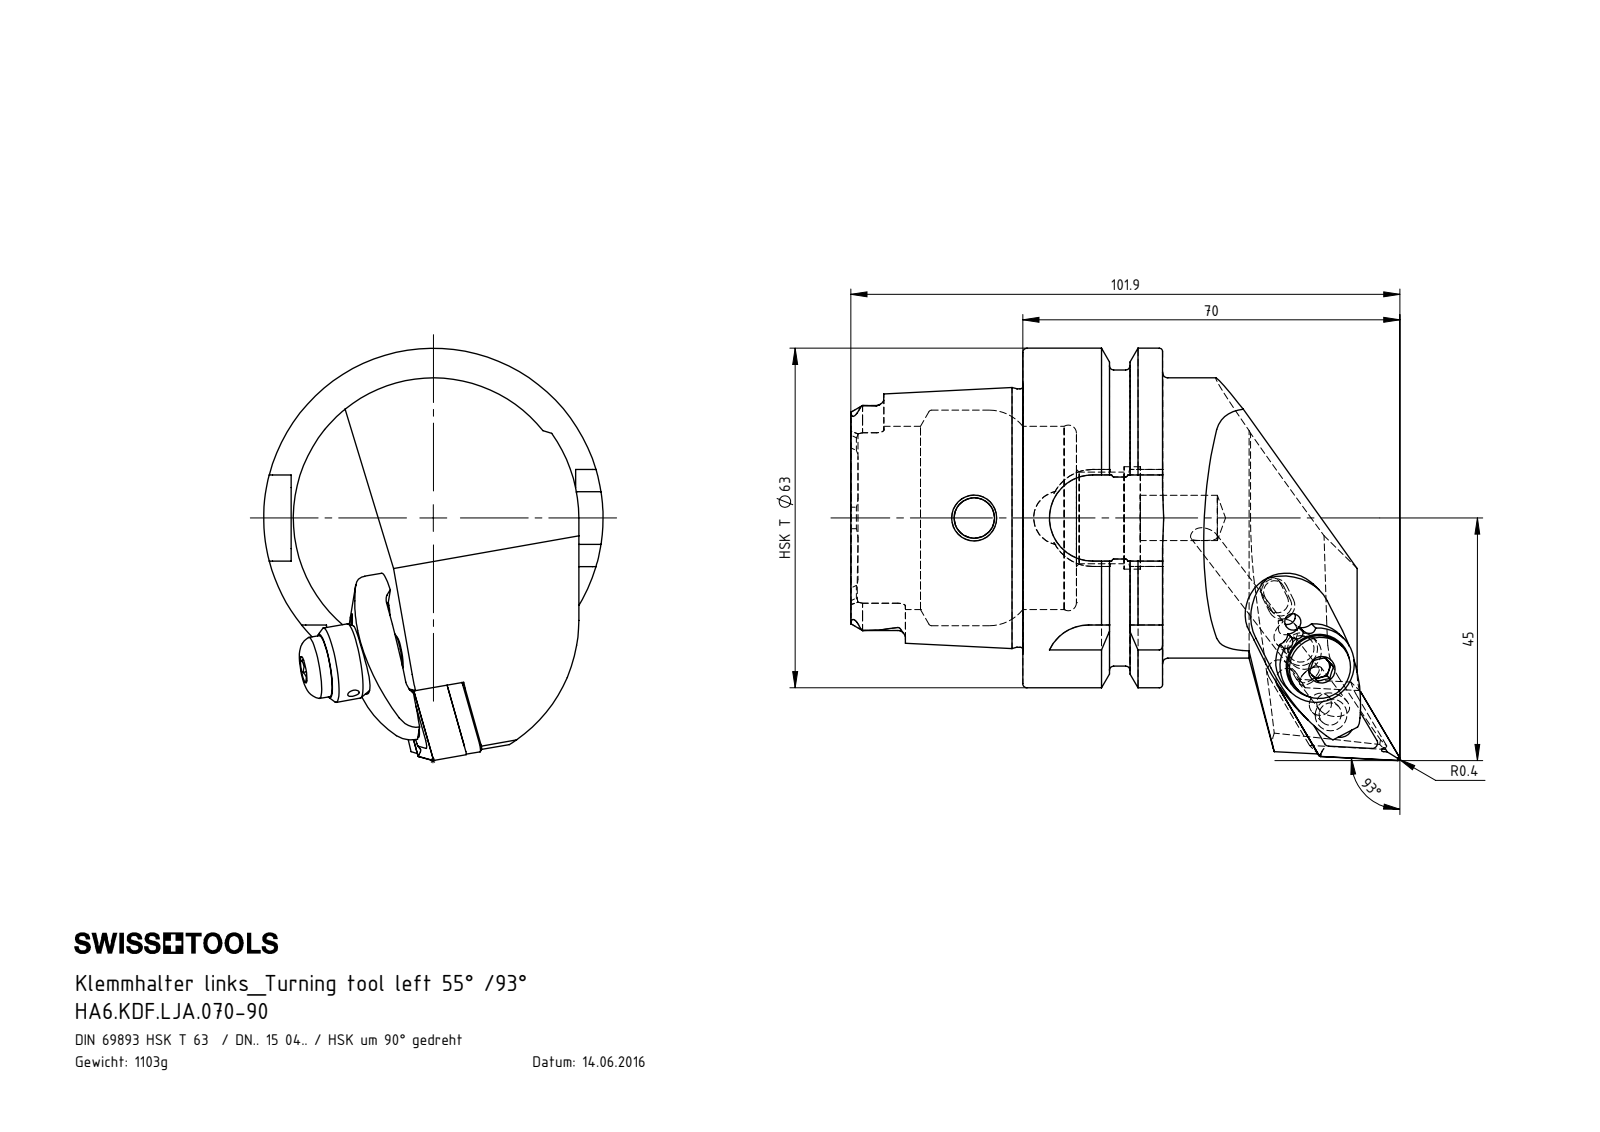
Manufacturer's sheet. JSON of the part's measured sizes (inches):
{"part_name": "WCC-ER2.001.010_A; HA6-KDF.LJA.070-90_A; KVT_MB_600_050; WCC-ER4.103.032_A (+6 more)", "step_written_by": "SolidWorks 2017 (AUTOMOTIVE_DESIGN)", "units": "inches", "bodies": {"solids": 10, "faces": 347, "planar": 123, "cylindrical": 100, "other": 124}, "overall_size": [4.012, 3.012, 2.48], "volume_in3": 8.615, "surface_area_in2": 53.74, "round_holes": [[0.079, 3], [0.165, 2], [0.197, 2], [0.276, 2], [0.118, 1], [0.157, 1], [0.203, 1], [0.244, 1], [0.252, 1], [0.295, 1], [0.331, 1], [0.335, 1]], "round_bosses_or_shafts": [[0.197, 2], [2.48, 1], [2.163, 1], [2.047, 1], [1.887, 1], [0.551, 1], [0.453, 1], [0.276, 1]], "partial_cylinders_radius": [[0.015, 6], [0.055, 6], [0.016, 4], [0.039, 4], [0.113, 4], [0.315, 4], [0.027, 3], [0.027, 3]], "face_to_face_distances": [1.022, 0.63, 0.392, 1.256, 1.648, 2.278, 0.238, 2.079, 0.125, 0.363], "hole_center_spacings": [0.315, 0.583, 0.59, 0.591, 0.906, 0.323]}
